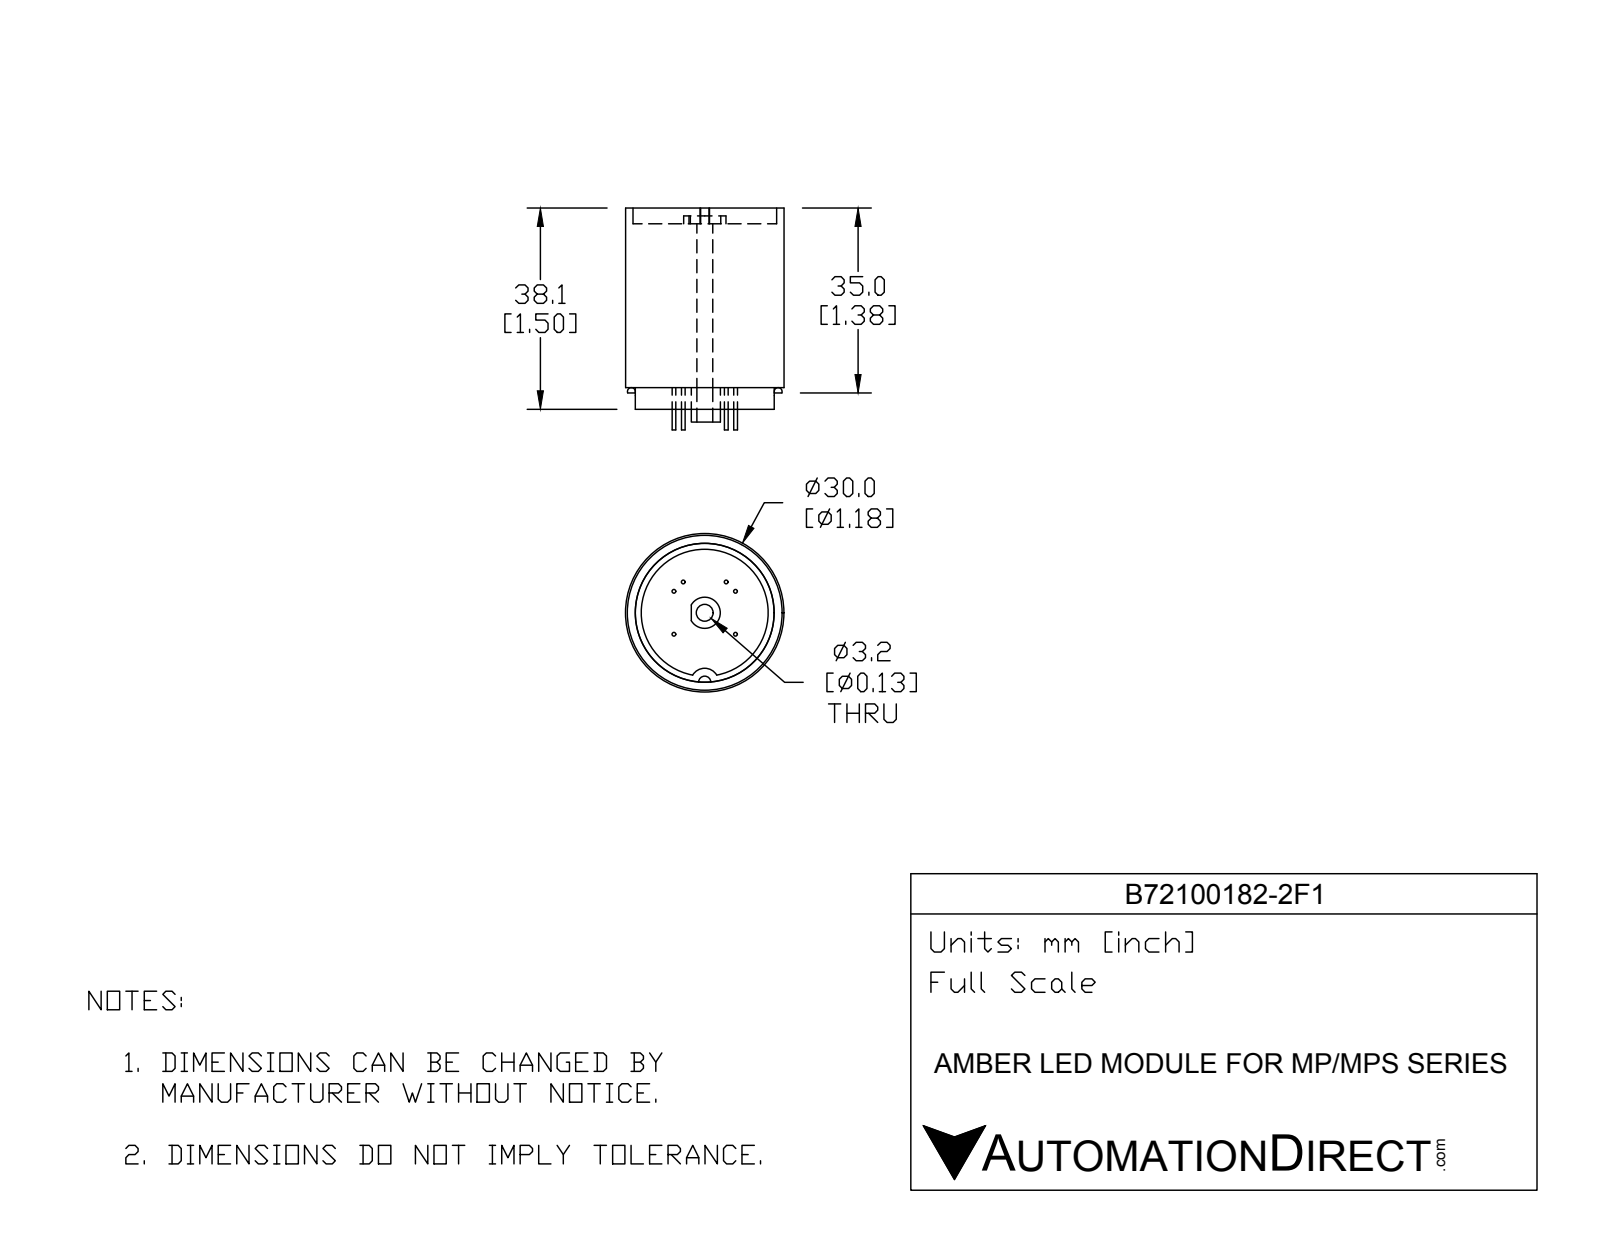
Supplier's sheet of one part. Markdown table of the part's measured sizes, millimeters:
| quantity | value |
| --- | --- |
| part name | B72100182-2F1 |
| STEP written by | SolidWorks 2016 (AUTOMOTIVE_DESIGN) |
| units | millimeters |
| bodies | 10 solids, 64 faces (25 planar, 35 cylindrical, 4 other) |
| overall size | 42 × 30 × 30 |
| volume | 22 787 mm³ |
| surface area | 6 668 mm² |
| round holes (diameter × count) | 3 × 1, 6.06 × 1, 24.04 × 1, 27.2 × 1 |
| round bosses / shafts (diameter × count) | 0.7 × 6, 30 × 1, 26.3 × 1, 8 × 1, 5.9 × 1 |
| partial cylindrical surfaces (radius × count) | 0.9 × 1, 1.15 × 1, 2.65 × 1 |
| main face-to-face distances | 31, 34, 3, 4.1, 35.1, 38.1, 1.5, 36.6, 32.5, 2.42 |
